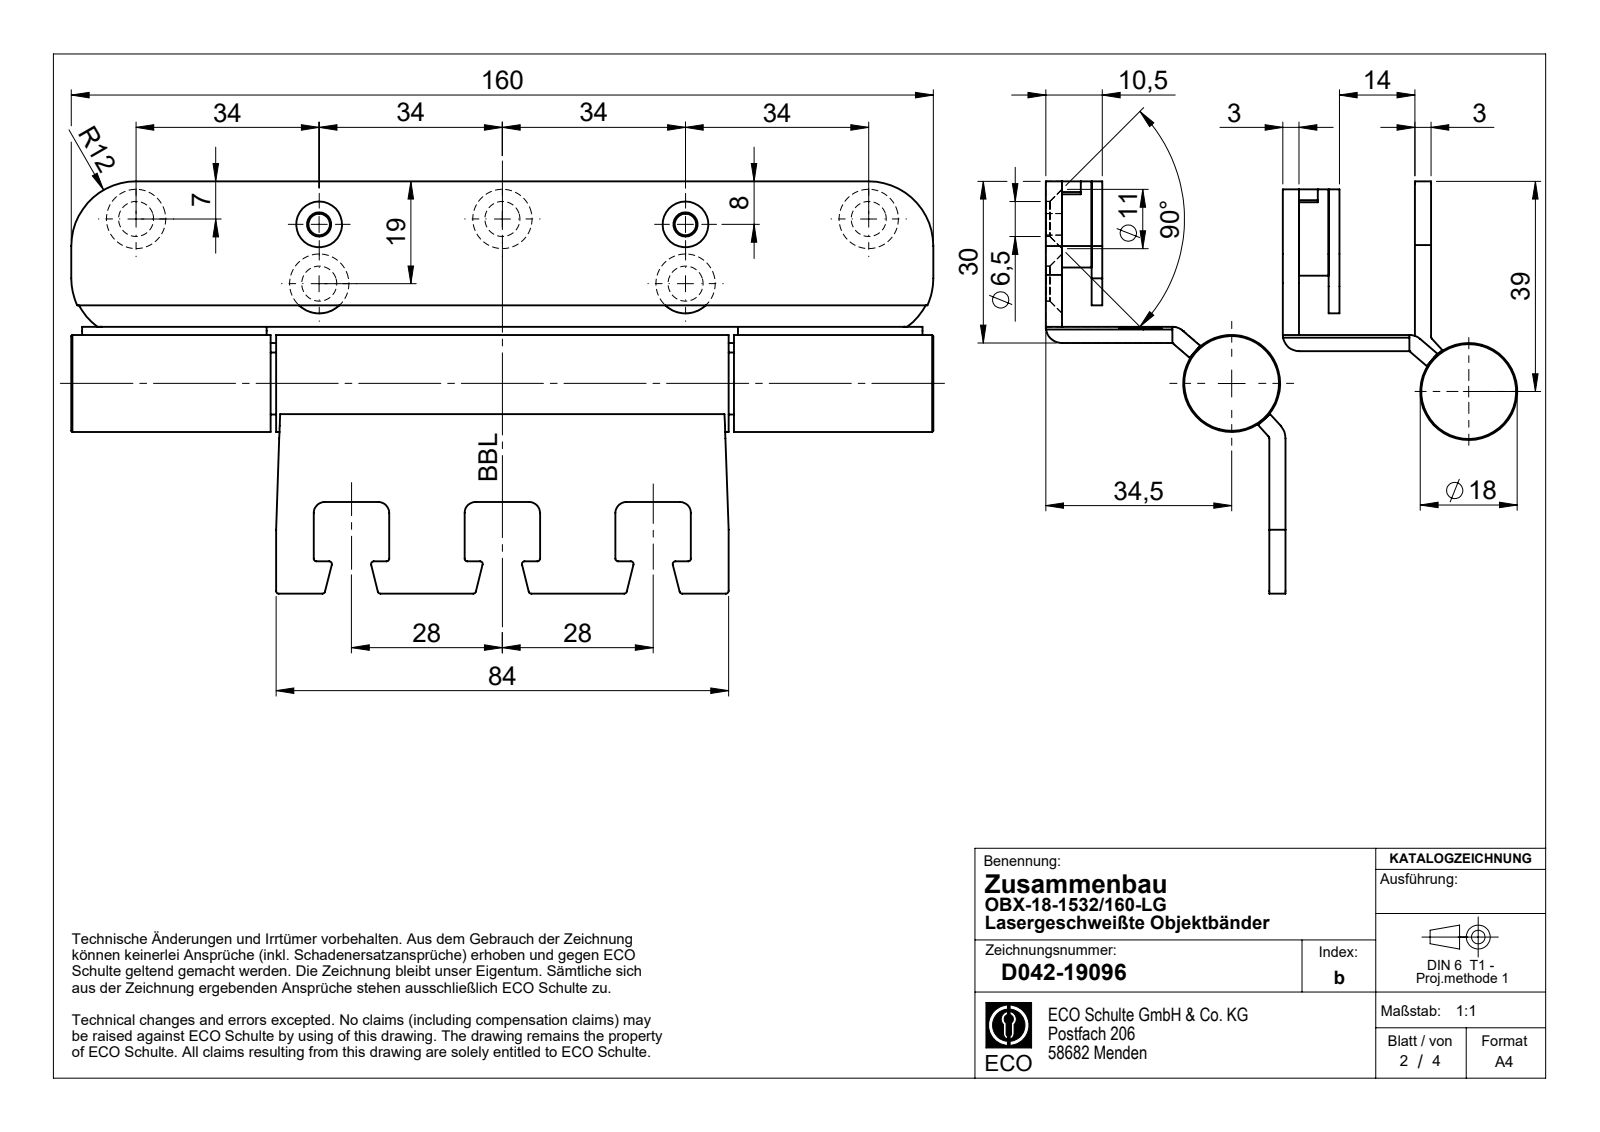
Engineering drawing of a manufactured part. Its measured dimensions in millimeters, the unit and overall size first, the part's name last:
Units: millimetres
Overall size (bounding box): 160 × 48 × 43.5
Round holes (diameter × count): ⌀6.5 ×5, ⌀2 ×2, ⌀4 ×2, ⌀5 ×2, ⌀0.5 ×1, ⌀4.5 ×1, ⌀7.9 ×1
Round bosses / shafts (diameter × count): ⌀7 ×2, ⌀18 ×1, ⌀12 ×1, ⌀11.8 ×1, ⌀11.5 ×1, ⌀7.7 ×1, ⌀4 ×1, ⌀1.65 ×1
Partial cylindrical surfaces — rounded edges, fillets, slot ends (radius × count): R0.5 ×21, R0.25 ×6, R2 ×6, R12 ×6, R3.5 ×5, R2.5 ×4, R0.68 ×2, R2.1 ×2
Main face-to-face distances: 3, 2, 5.5, 8.5, 24.5, 7.5, 10.5, 14, 16, 4
Hole centre spacings: 34.01, 36.06, 68, 11, 68.88, 102, 102.7, 1.95
Volume: 83 350 mm³ · Surface area: 55 649 mm²
Bodies: 13 solids, 612 faces (333 planar, 178 cylindrical, 101 other)
Part name (STEP PRODUCT): OBX-18-1532-160-LG_D042-19096; B01572; B03164; D044-14309 (+6 more)
STEP written by: SolidWorks 2020 (CONFIG_CONTROL_DESIGN)
